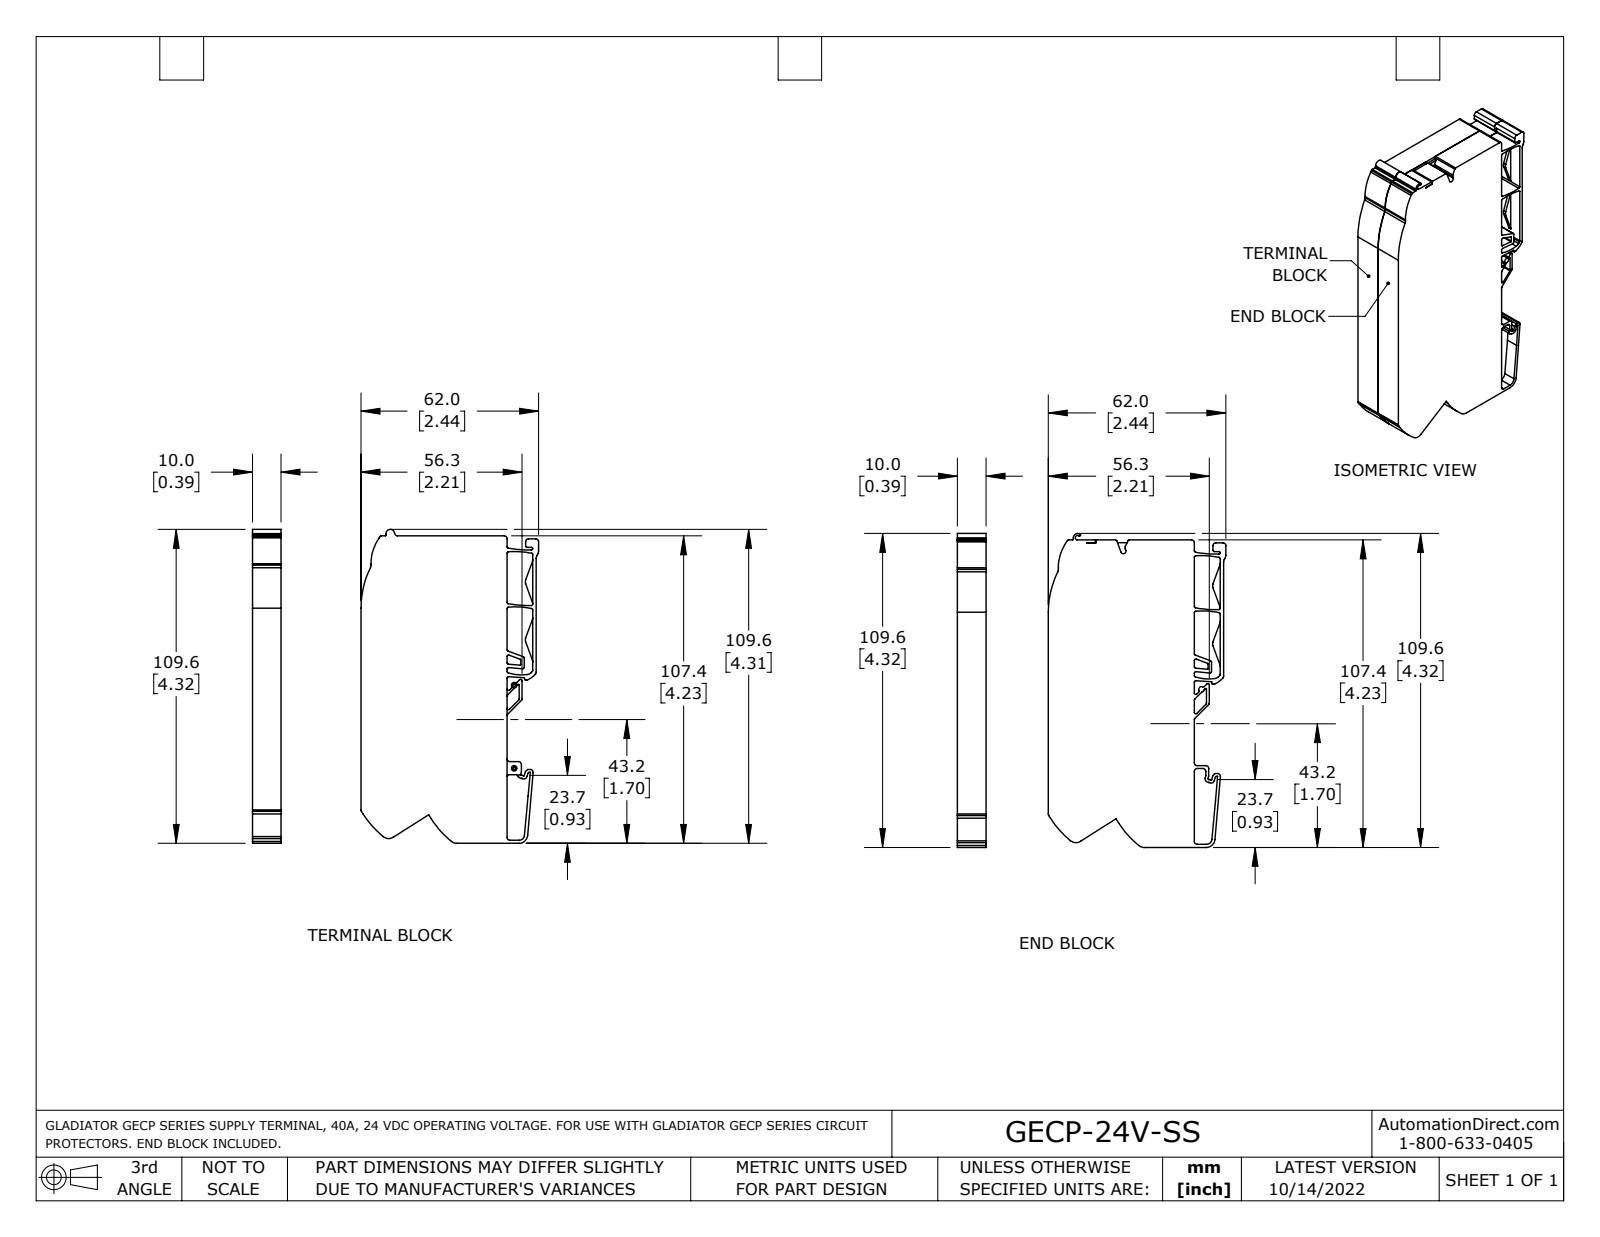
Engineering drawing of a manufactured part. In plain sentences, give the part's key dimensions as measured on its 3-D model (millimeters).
The part is named "GECP-24V-SS". Its 3-D file was written by "SolidWorks 2021 (AUTOMOTIVE_DESIGN)". It is 2 solids with 638 faces: 312 planar, 299 cylindrical and 27 other. Overall it measures 243.2 by 130 by 110.2 millimeters. Its volume is 107 900 cubic millimeters and its surface area 35 360 square millimeters. Round bosses or shafts: 3 of diameter 1.9. Partial cylindrical surfaces (rounded edges, fillets, slot ends): 75 of radius 0.5, 29 of radius 1, 24 of radius 0.3, 20 of radius 2, 15 of radius 0.2, 13 of radius 0.3, 8 of radius 3, 4 of radius 1.2. The main face-to-face distances are 120, 10, 130, 120.2, 110.3, 9.8, 181.2, 10, 120, 110.1.
